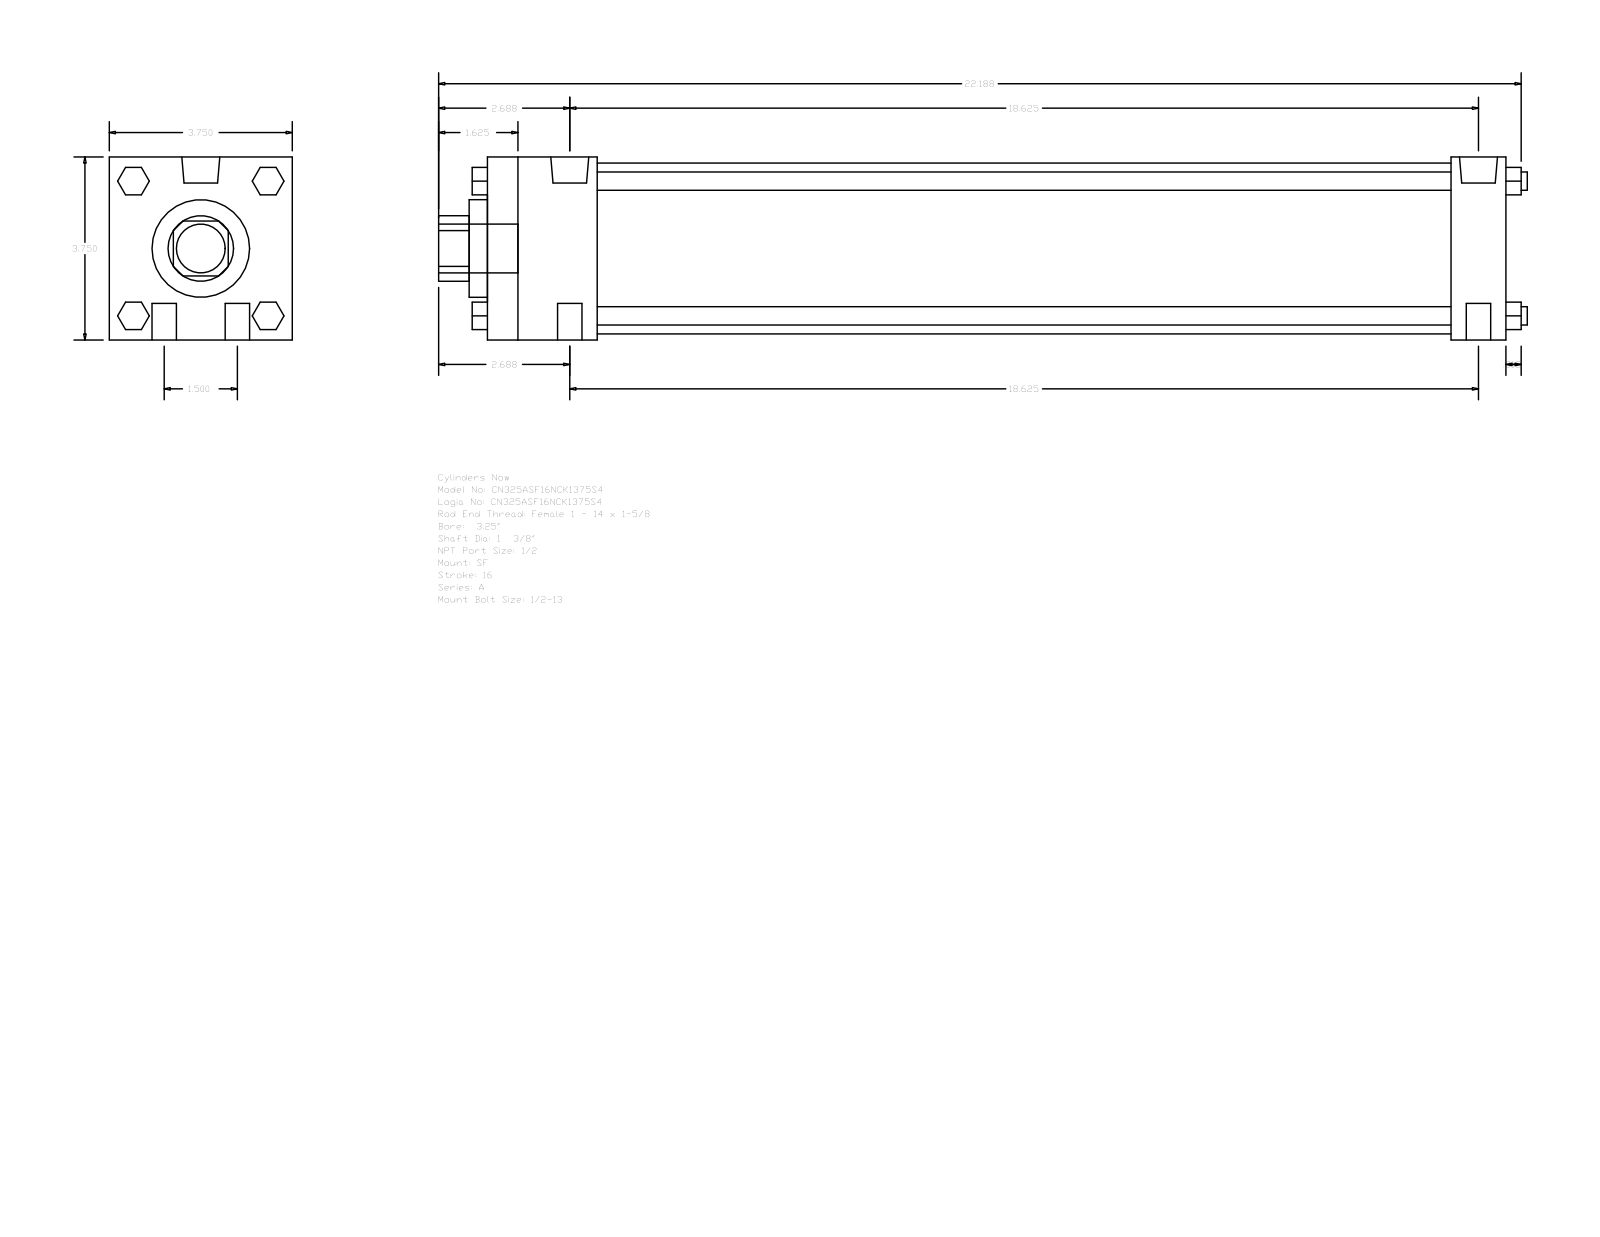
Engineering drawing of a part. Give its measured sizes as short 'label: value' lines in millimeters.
name: A_SF__0325_1.375
written by: GSSL Pune (CONFIG_CONTROL_DESIGN)
unit: mm
bodies: 0 solids, 124 faces (94 planar, 30 cylindrical, 0 other)
size: 566.74 × 95.25 × 95.25
holes: 1× ⌀34.92, 1× ⌀50.8, 1× ⌀88.9
bosses: 4× ⌀12.7, 4× ⌀9.53, 2× ⌀19.77, 2× ⌀8.73, 1× ⌀25.4
rounds: 1× R17.06
face distances: 95.24, 530.22, 28.57, 501.65, 57.15, 444.5, 473.07, 9.52, 66.67, 511.17
